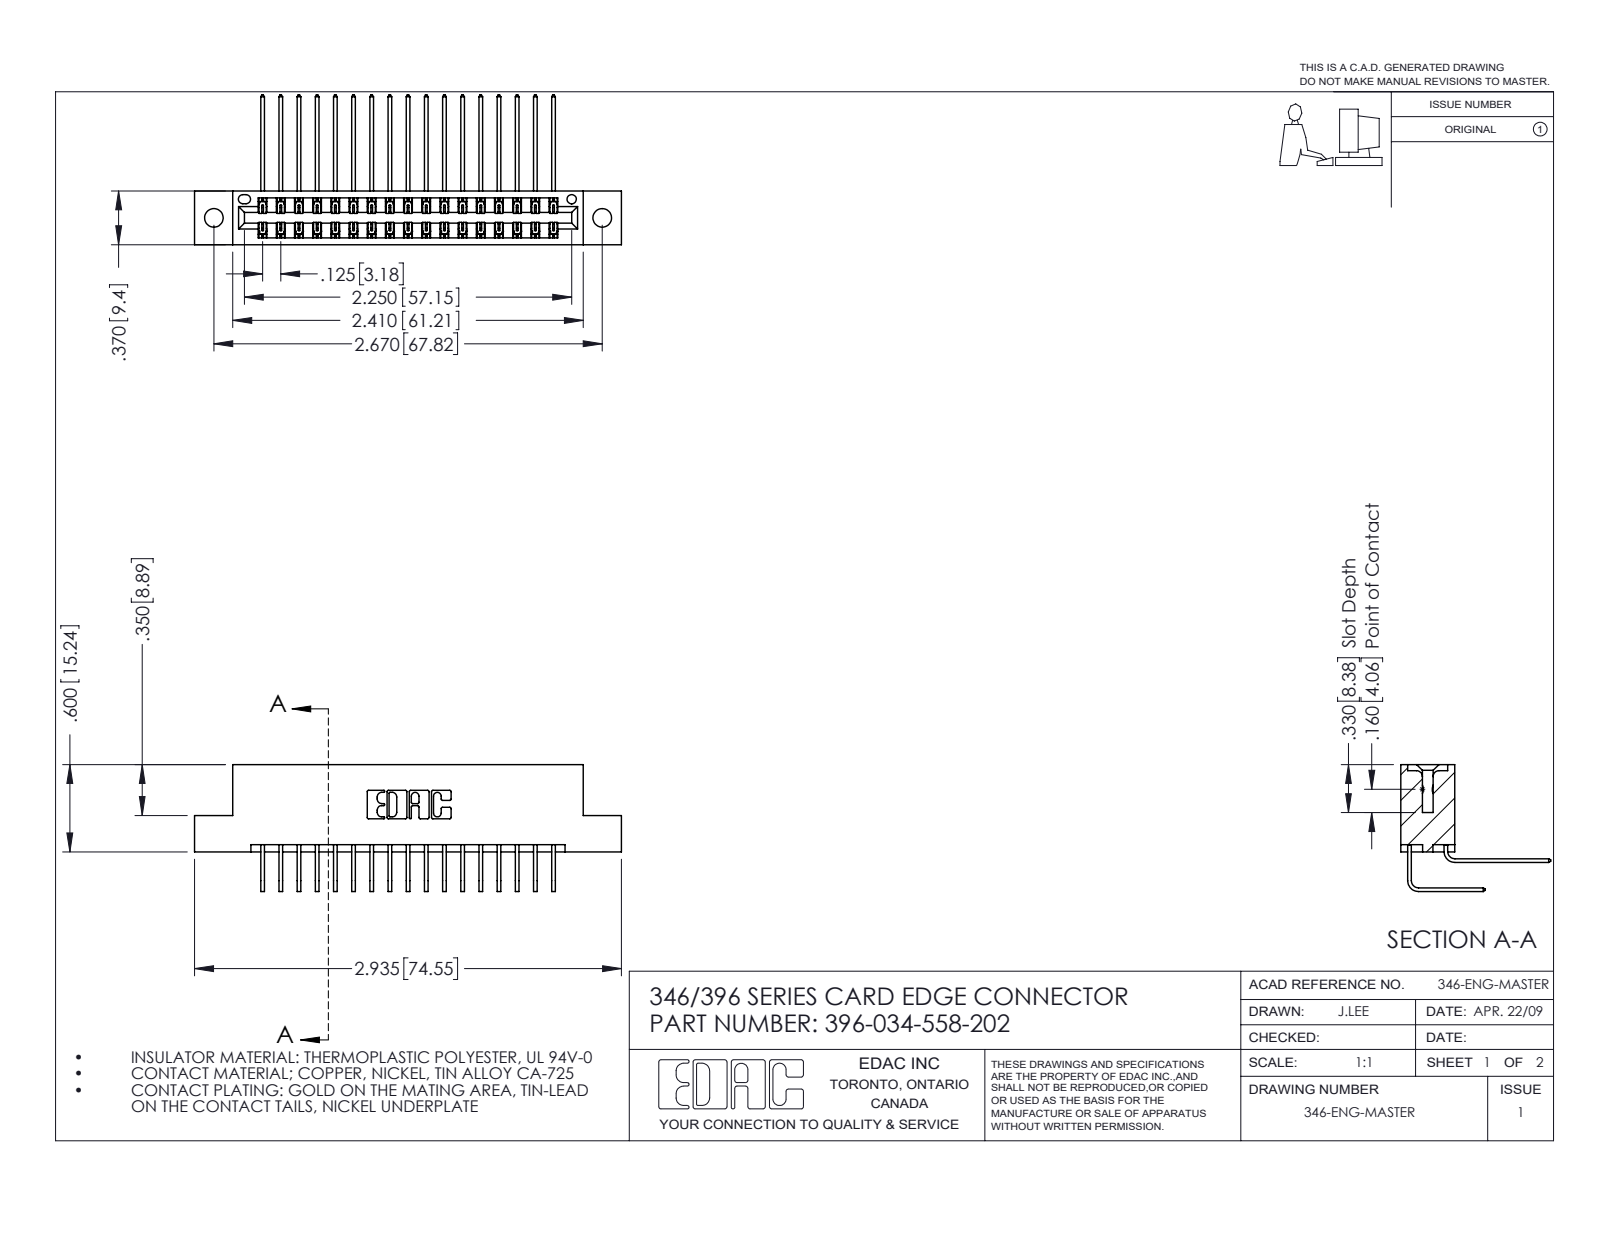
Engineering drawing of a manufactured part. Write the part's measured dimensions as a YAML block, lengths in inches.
part_name: "345-292-001_558 Tail - 2; 345-292-001_558 559 Tail - 1; 346 Part_Flush Mounting Lugs - 0.128 Dia; 396-034-558-202"
step_written_by: "SolidWorks 2016 (CONFIG_CONTROL_DESIGN)"
units: inches
bodies: {solids: 35, faces: 1958, planar: 1334, cylindrical: 624, other: 0}
overall_size: [2.935, 1.03, 0.873]
volume: 0.441
surface_area: 15.85
round_holes:
  - {diameter: 0.128, count: 2}
  - {diameter: 0.064, count: 1}
partial_cylinders:
  - {radius: 0.006, count: 51}
  - {radius: 0.01, count: 22}
  - {radius: 0.007, count: 6}
  - {radius: 0.031, count: 6}
  - {radius: 0.026, count: 3}
  - {radius: 0.014, count: 2}
  - {radius: 0.022, count: 2}
  - {radius: 0.024, count: 2}
face_to_face_distances: [0.322, 0.048, 0.25, 0.025, 0.37, 0.298, 0.072, 0.275, 0.148, 0.222]
hole_center_spacings: [0.246, 2.463, 2.67]
